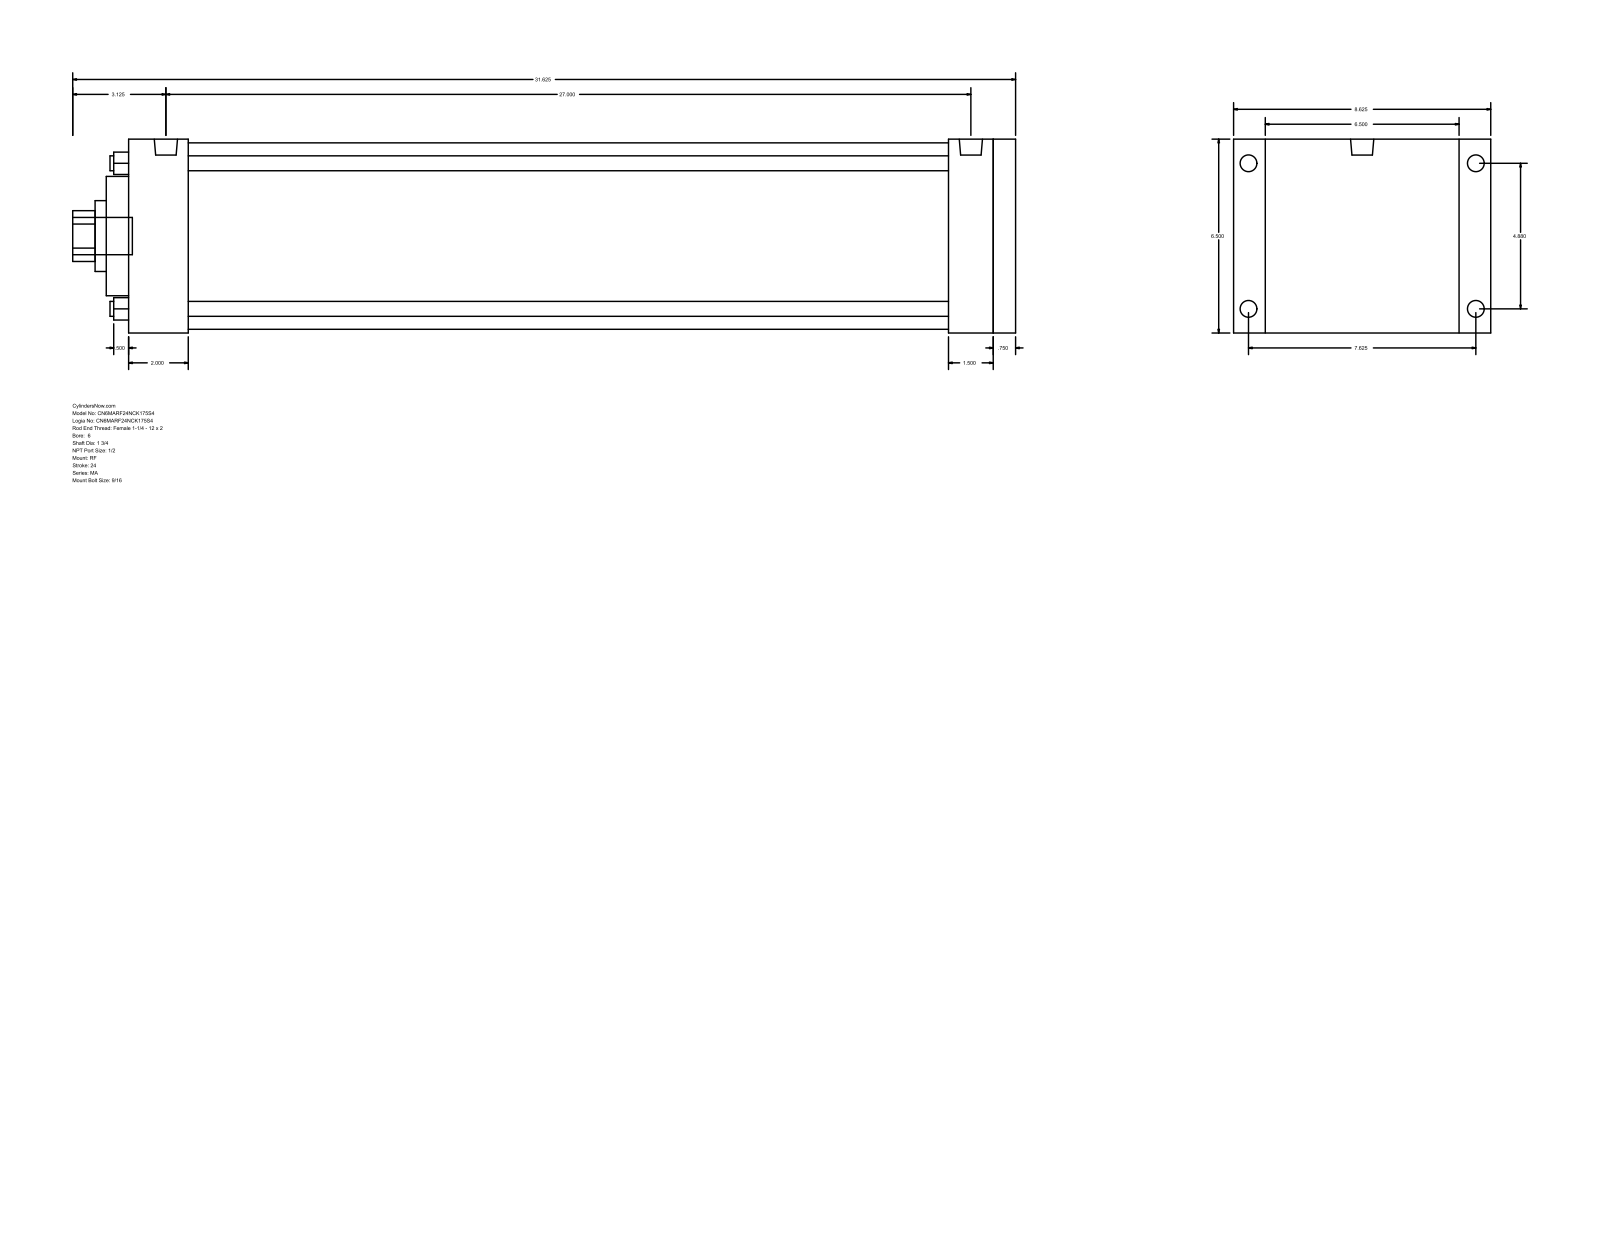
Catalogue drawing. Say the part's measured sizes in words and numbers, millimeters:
The part is named "MA_RF__0600_1.75". Its 3-D file was written by "GSSL Pune (CONFIG_CONTROL_DESIGN)". It is 0 solids with 94 faces: 65 planar, 29 cylindrical and 0 other. Overall it measures 803.27 by 219.07 by 165.1 millimeters. Round holes: 4 of diameter 12.7, 1 of diameter 44.45, 1 of diameter 60.33, 1 of diameter 101.6, 1 of diameter 158.75. Round bosses or shafts: 4 of diameter 17.46, 4 of diameter 14.29, 2 of diameter 19.77, 1 of diameter 31.75. Partial cylindrical surfaces (rounded edges, fillets, slot ends): 1 of radius 21.63. The main face-to-face distances are 165.1, 755.65, 19.04, 736.61, 19.05, 50.8, 685.81, 704.85, 698.5, 647.7. The hole center spacings are 87.65, 123.96, 175.31.
